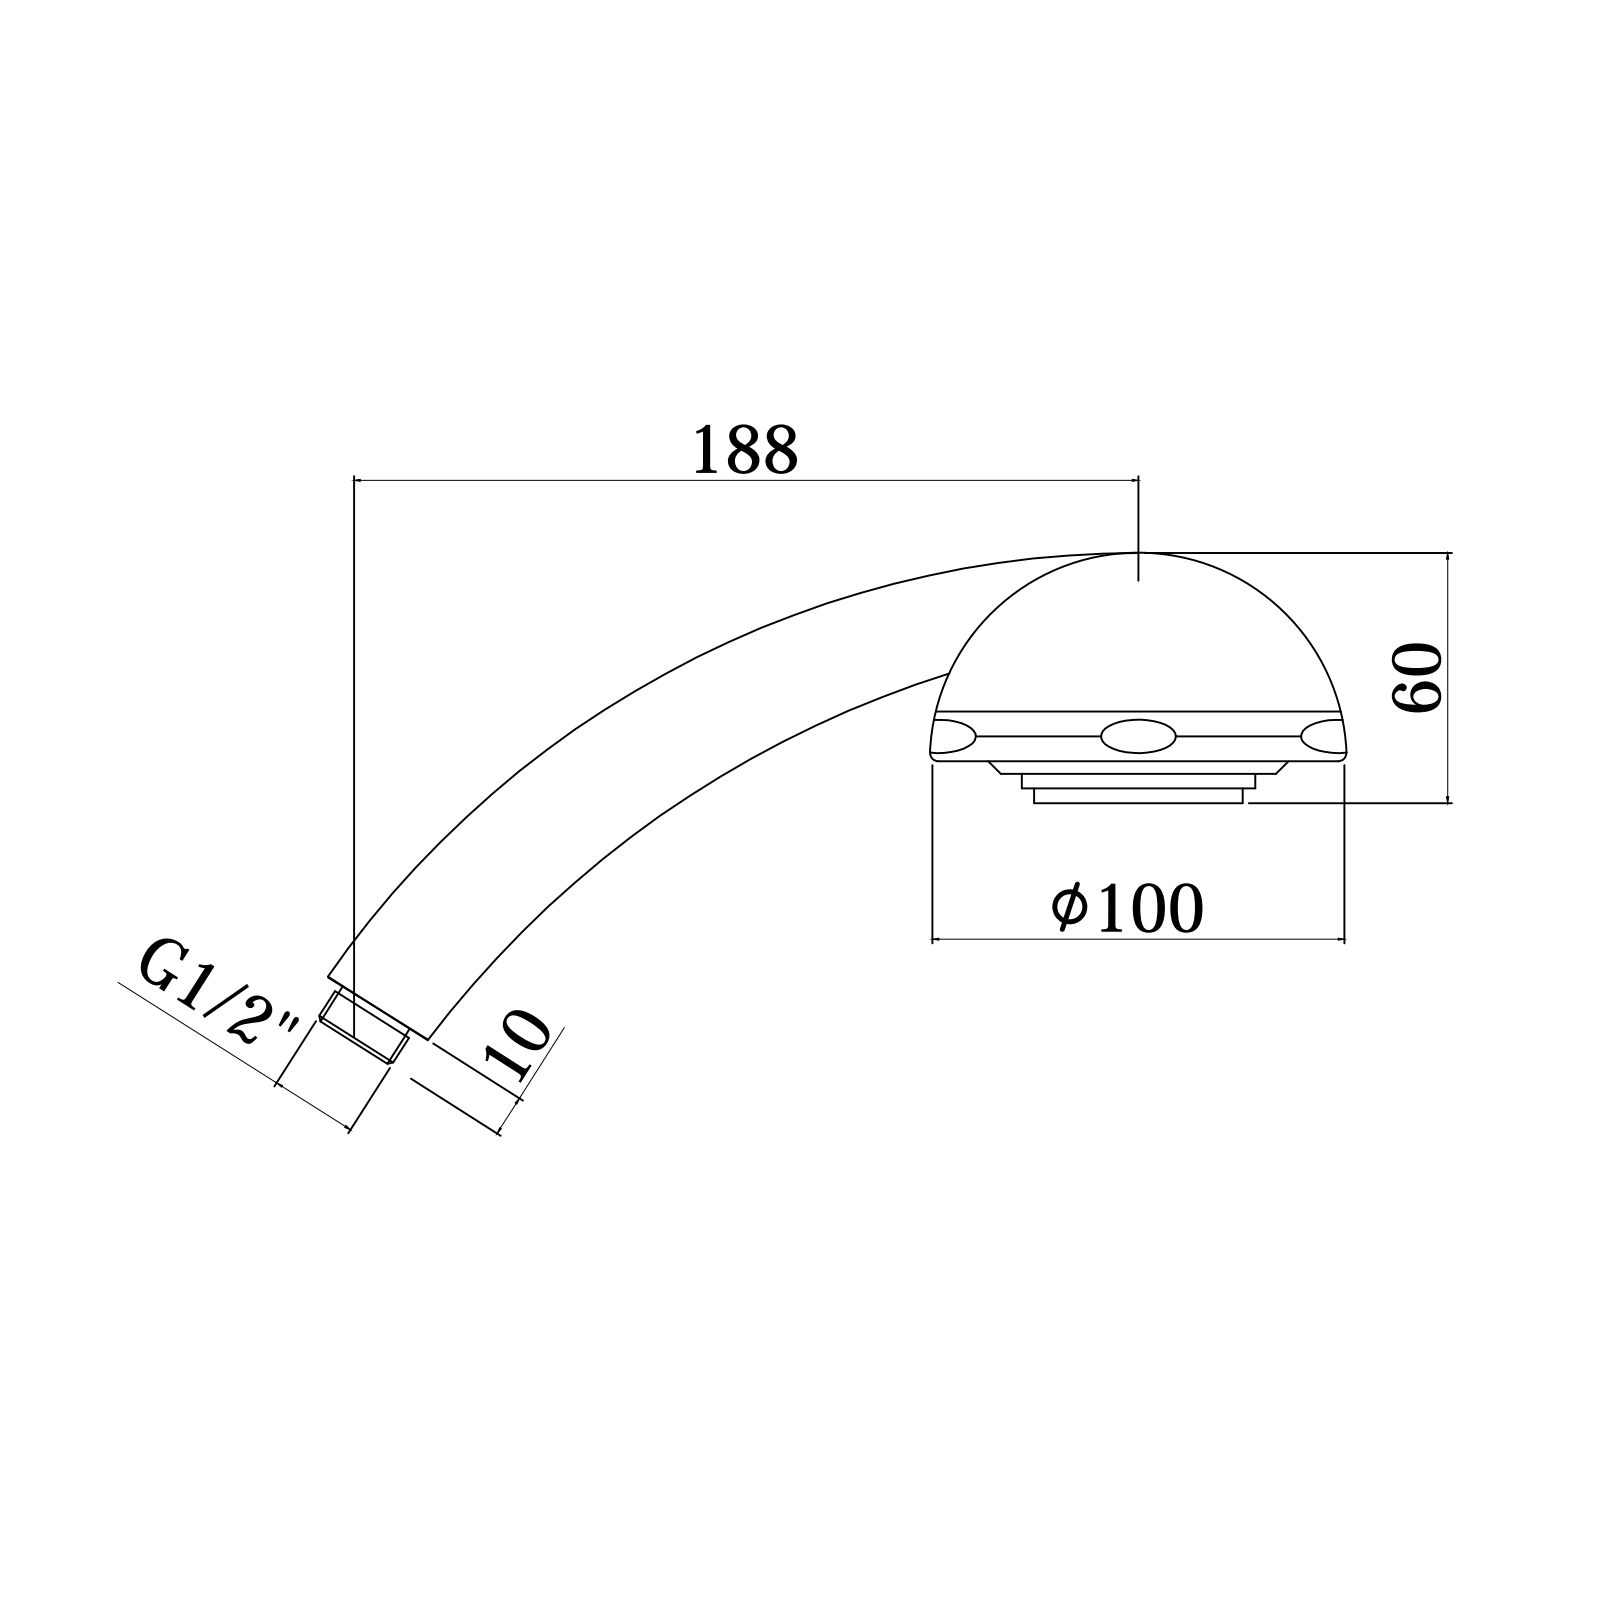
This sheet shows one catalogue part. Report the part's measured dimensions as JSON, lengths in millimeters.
{"part_name": "ZDOC045CR", "step_written_by": "CREO PARAMETRIC BY PTC INC, 2020044 (CONFIG_CONTROL_DESIGN)", "units": "millimeters", "bodies": {"solids": 1, "faces": 1739, "planar": 397, "cylindrical": 429, "other": 913}, "overall_size": [244.23, 104.84, 96.7], "volume_mm3": 178364, "surface_area_mm2": 118725, "round_holes": [[1.7, 10], [4.2, 10], [4.8, 10], [2.8, 4], [3.5, 1], [8, 1], [9.75, 1], [12, 1], [14, 1], [19.1, 1], [25.8, 1], [26.5, 1]], "round_bosses_or_shafts": [[3.4, 40], [91.5, 1], [85.8, 1], [85.2, 1], [75.2, 1], [72.3, 1], [71, 1], [69.6, 1]], "partial_cylinders_radius": [[0.3, 16], [1, 13], [4, 10], [2.6, 8], [0.5, 2], [4.44, 2], [6, 2], [24.7, 2]], "face_to_face_distances": [2.5, 8.4, 12.8, 11, 2.9, 9.9, 2, 5.6, 15.6, 3], "hole_center_spacings": [11.99, 28.64, 18.78, 24.72, 8, 11, 17.8, 19]}
